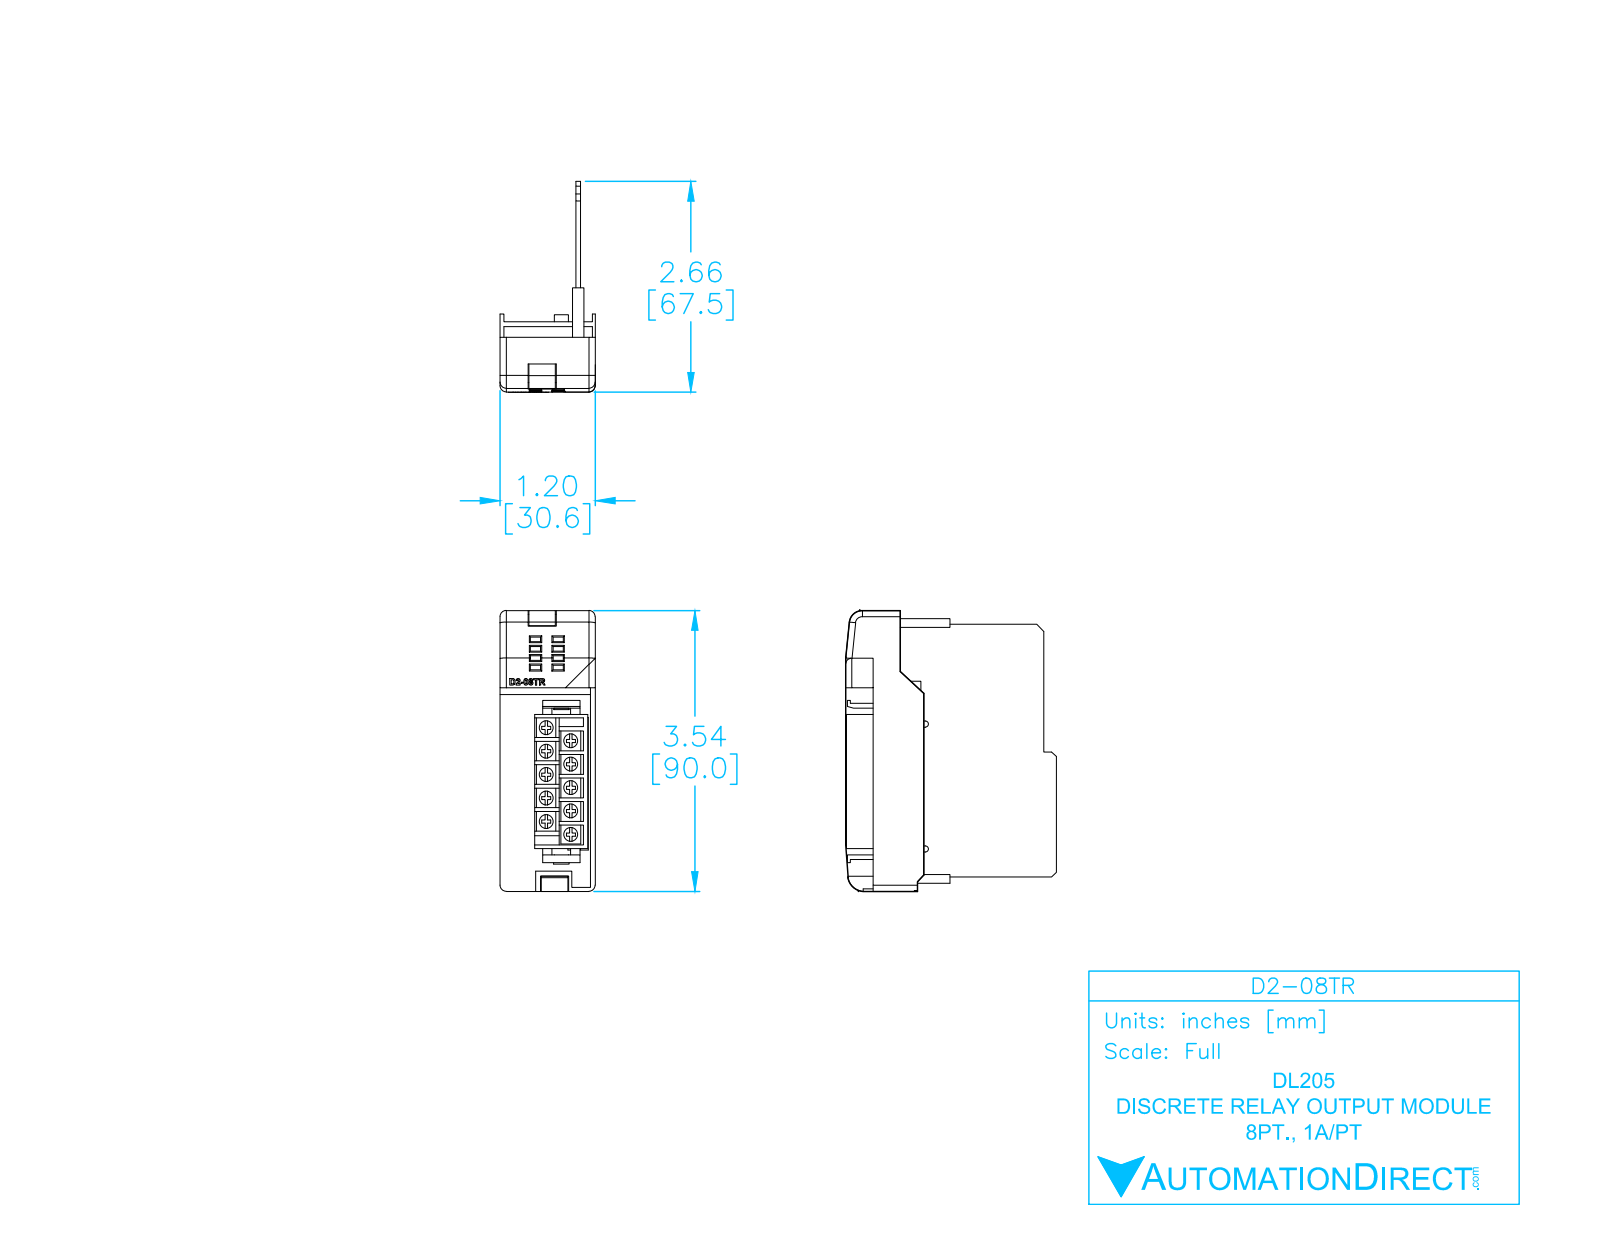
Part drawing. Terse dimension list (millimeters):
name: D2-08TR_ModuleCase_light_NEW
written by: SolidWorks 2009 (AUTOMOTIVE_DESIGN)
unit: mm
bodies: 6 solids, 572 faces (399 planar, 75 cylindrical, 98 other)
size: 90 × 67.56 × 30.55
volume: 25 372 mm³; area: 28 529 mm²
bosses: 10× ⌀4.5
rounds: 16× R0.35, 9× R2, 2× R0.25, 2× R1, 2× R1.25, 1× R4.12, 1× R5.39
face distances: 1.5, 4.72, 6.22, 2.62, 2.1, 4.12, 3.5, 3.22, 0.6, 2
